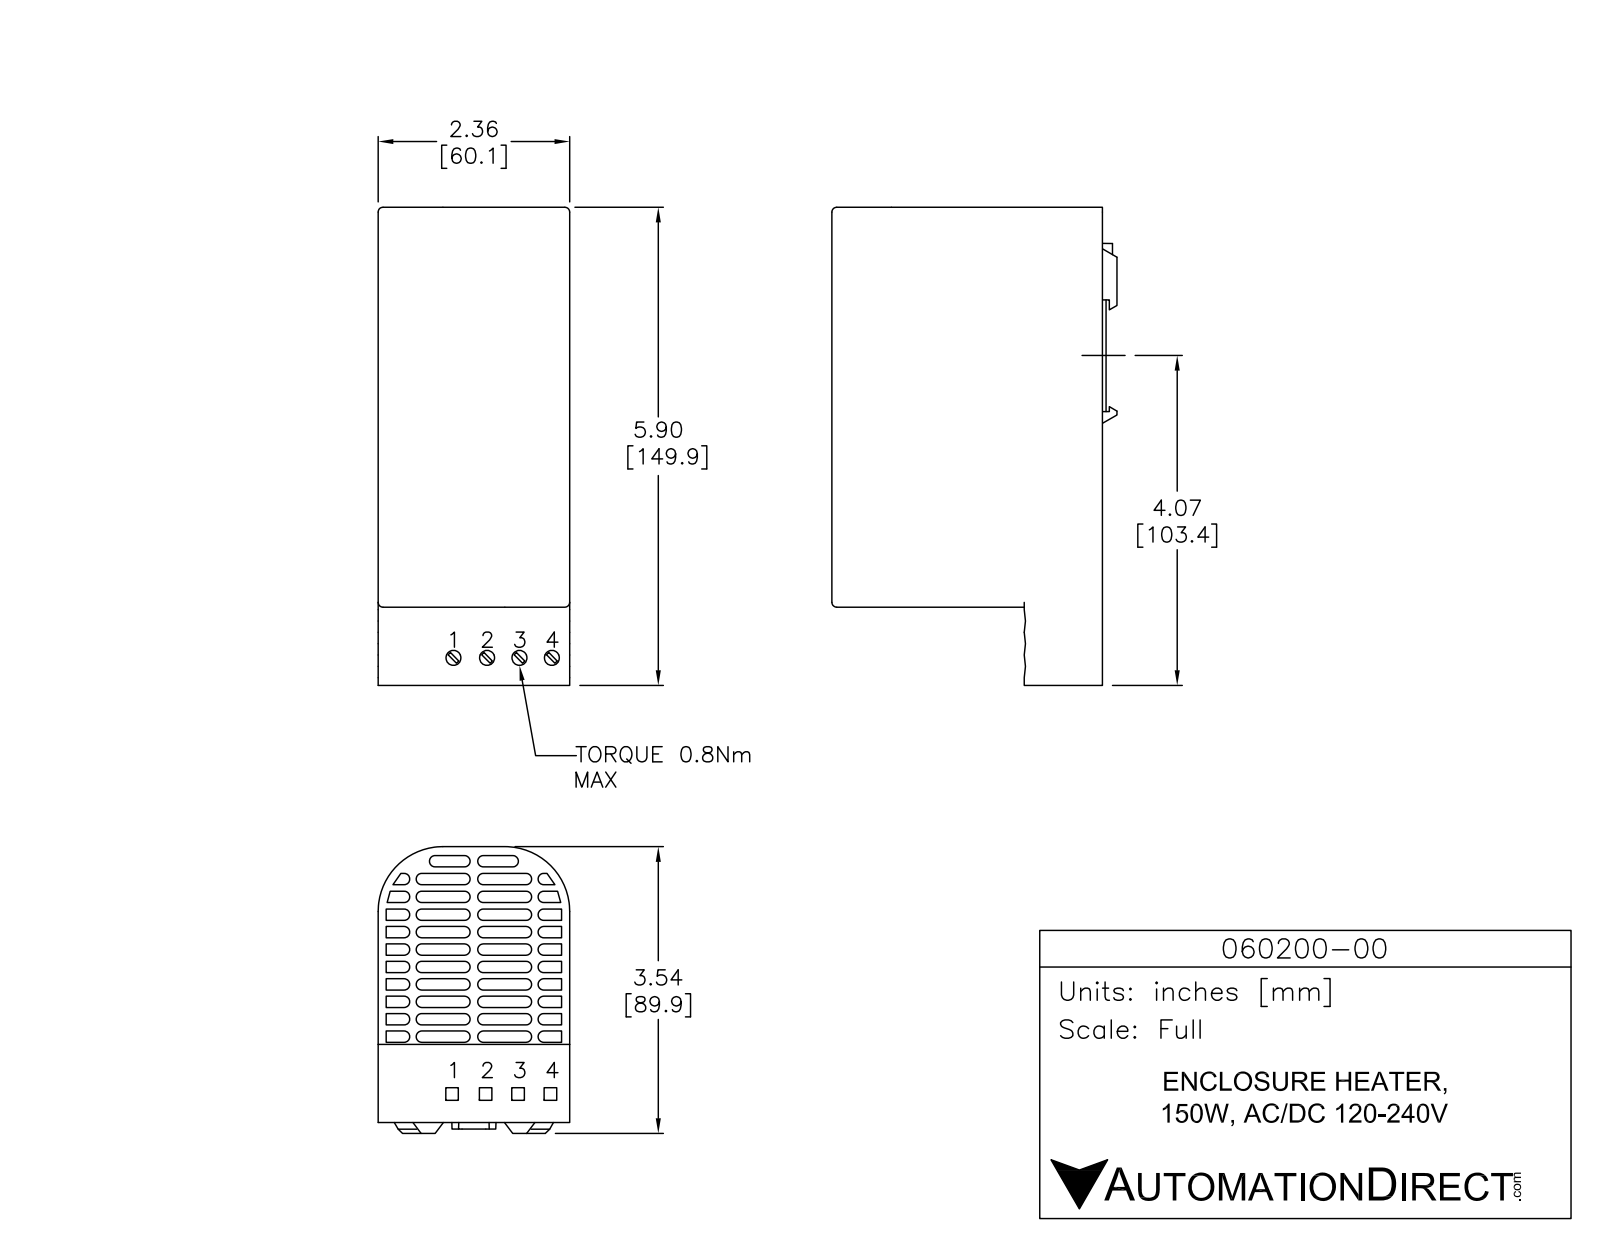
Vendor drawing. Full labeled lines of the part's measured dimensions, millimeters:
Part name (STEP PRODUCT): 060200-00
STEP written by: SolidWorks 2013 (AUTOMOTIVE_DESIGN)
Units: millimetres
Bodies: 1 solid, 859 faces (643 planar, 210 cylindrical, 6 other)
Overall size (bounding box): 149.9 × 90.9 × 59.7
Volume: 632 700 mm³ · Surface area: 72 900 mm²
Round holes (diameter × count): ⌀4.7 ×4
Partial cylindrical surfaces — rounded edges, fillets, slot ends (radius × count): R1.8 ×88, R0.9 ×18, R1.5 ×6, R20.3 ×2
Main face-to-face distances: 0.8, 1.5, 59.3, 58.6, 2.3, 4.6, 1.5, 3.1, 2.3, 3.8
Hole centre spacings: 10.2, 20.3, 30.5
